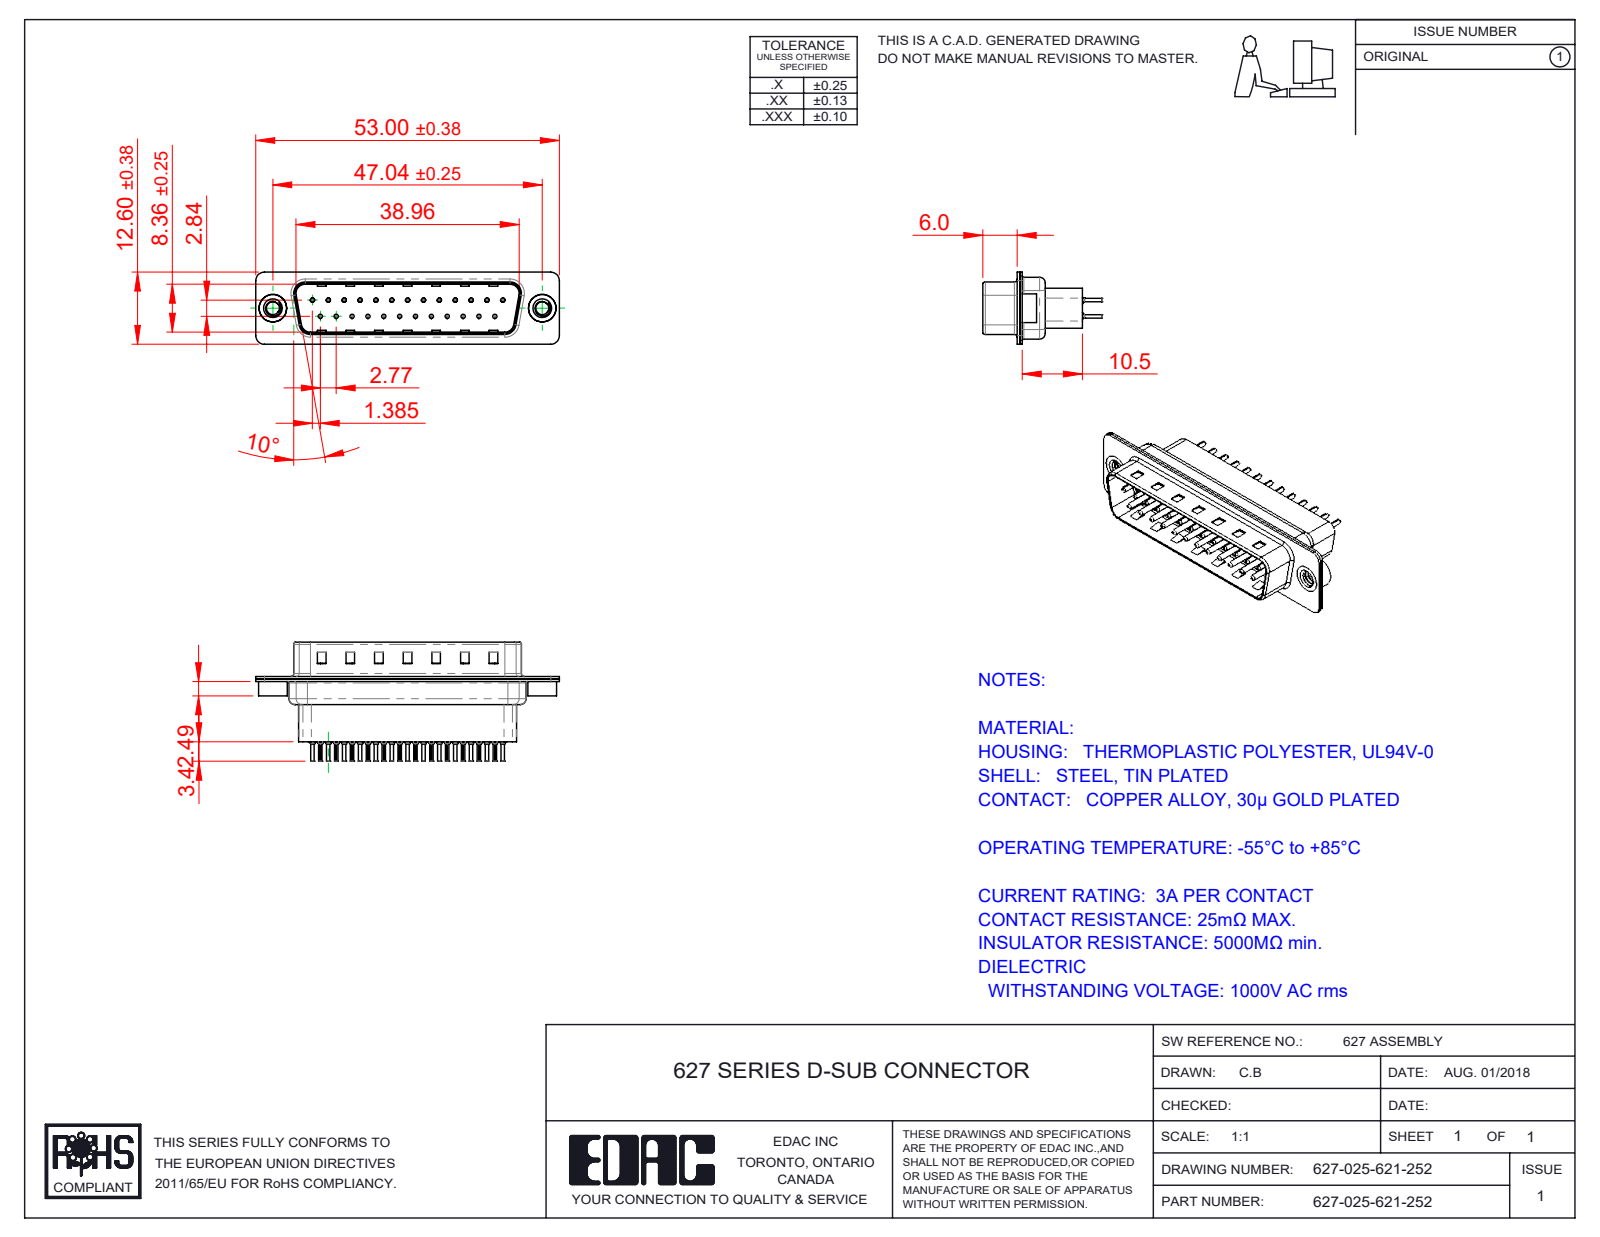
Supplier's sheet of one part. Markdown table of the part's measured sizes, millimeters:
| quantity | value |
| --- | --- |
| part name | 627 Shell Front_25 Contacts; 627-025-621-052; 627 Shell Rear_25 Contacts; 627 Housing_25 HP (+3 more) |
| STEP written by | SolidWorks 2020 (CONFIG_CONTROL_DESIGN) |
| units | millimeters |
| bodies | 30 solids, 2822 faces (771 planar, 1060 cylindrical, 991 other) |
| overall size | 53 × 20.8 × 12.6 |
| volume | 3 793 mm³ |
| surface area | 9 767 mm² |
| round holes (diameter × count) | 0.2 × 25, 0.35 × 25, 1.1 × 25, 1.6 × 25, 2.26 × 2, 4 × 2, 4.8 × 2 |
| round bosses / shafts (diameter × count) | 2 × 25, 1.5 × 25, 0.75 × 25, 0.6 × 25, 5 × 2, 4.9 × 2 |
| partial cylindrical surfaces (radius × count) | 0.1 × 50, 1.5 × 16, 2 × 12, 0.5 × 8, 1.6 × 8, 0.25 × 4, 0.6 × 4, 0.65 × 4 |
| main face-to-face distances | 0.4, 0.45, 0.82, 9.58, 0.68, 7.68, 1.5, 0.9, 1.08, 8.08 |
| hole center spacings | 3.16, 8.31, 2.77, 5.54, 11.08, 16.62, 5.03, 5.04 |
